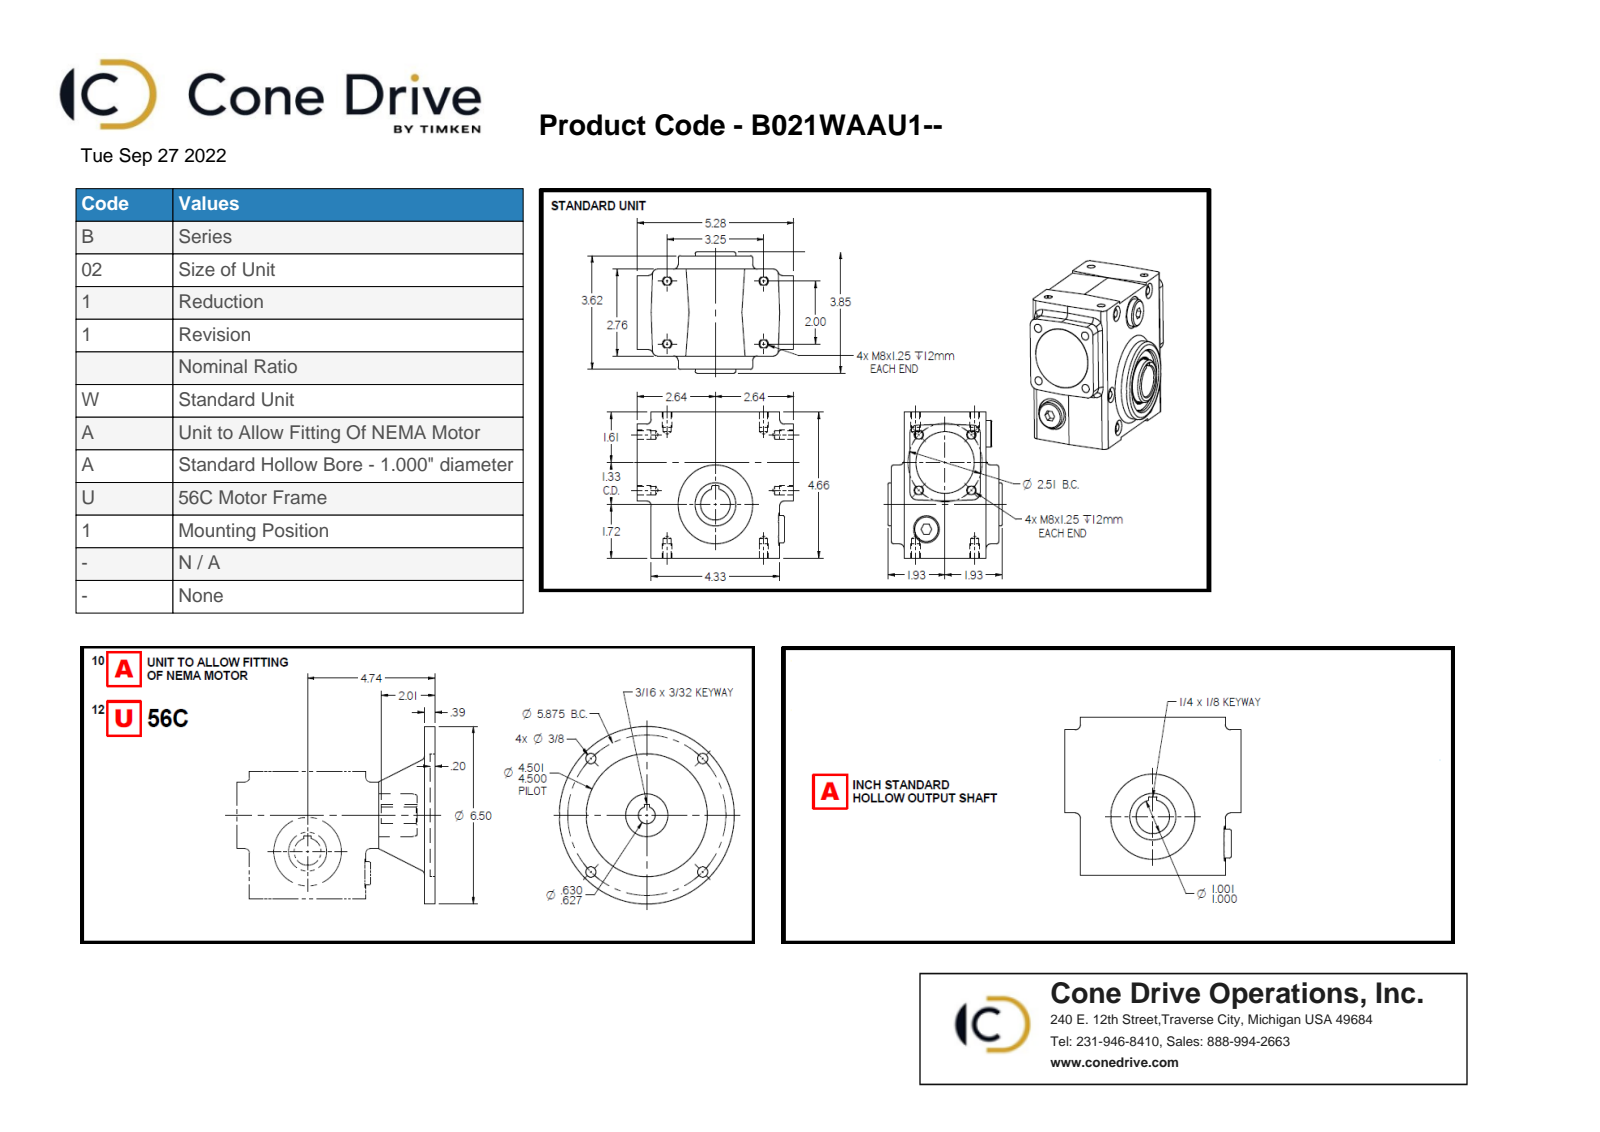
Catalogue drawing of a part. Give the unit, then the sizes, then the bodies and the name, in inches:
Units: inches
Overall size (bounding box): 7.378 × 6.5 × 6.5
Round holes (diameter × count): ⌀0.492 ×6, ⌀0.262 ×4, ⌀0.272 ×4, ⌀0.346 ×4, ⌀0.378 ×4, ⌀1.024 ×2, ⌀0.5 ×1, ⌀0.628 ×1, ⌀1 ×1, ⌀1.11 ×1, ⌀1.118 ×1, ⌀1.378 ×1
Round bosses / shafts (diameter × count): ⌀0.394 ×6, ⌀0.236 ×6, ⌀0.506 ×4, ⌀0.02 ×3, ⌀0.866 ×2, ⌀6.5 ×1, ⌀2.513 ×1, ⌀1.969 ×1
Partial cylindrical surfaces — rounded edges, fillets, slot ends (radius × count): R0.157 ×12, R0.157 ×4, R0.236 ×4, R0.295 ×4, R0.008 ×2, R0.024 ×2, R0.276 ×1, R0.278 ×1
Main face-to-face distances: 0.394, 2.759, 0.197, 1.708, 2.102, 4.66, 5.277, 4.656, 1.905, 0.157
Hole centre spacings: 3.194, 1.253, 1.685, 1.772, 2.937, 4.154, 4.19, 1.267
Volume: 68.41 in³ · Surface area: 320.1 in²
Bodies: 11 solids, 500 faces (267 planar, 125 cylindrical, 108 other)
Part name (STEP PRODUCT): B021120.WAAU1; B02-1-CP; B02U-CP
STEP written by: Solid Edge (AUTOMOTIVE_DESIGN)
